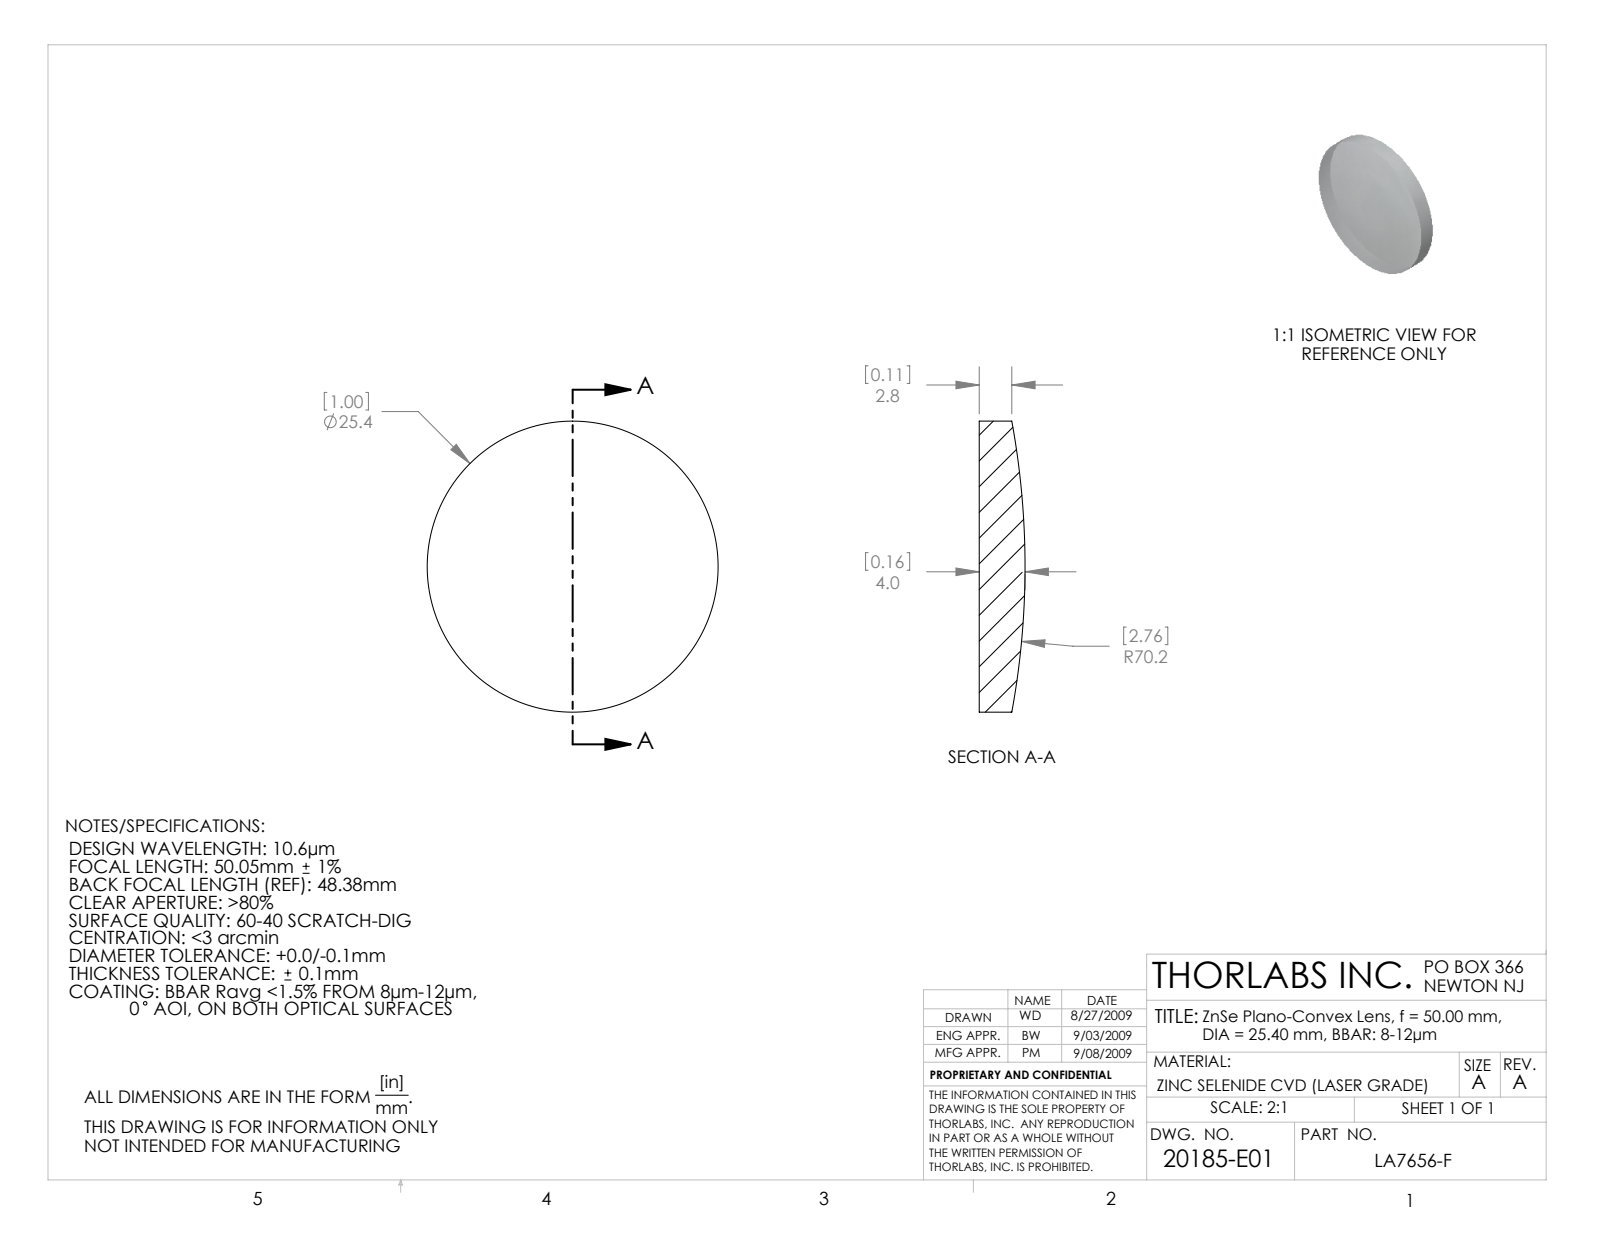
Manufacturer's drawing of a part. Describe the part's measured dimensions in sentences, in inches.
The part is named "20185-E0W". Its 3-D file was written by "SolidWorks 2007 (CONFIG_CONTROL_DESIGN)". It is 1 solid with 5 faces: 1 planar, 2 cylindrical and 2 other. Overall it measures 1 by 1 by 0.157 inches. Its volume is 0.106 cubic inches and its surface area 1.928 square inches. Round bosses or shafts: 1 of diameter 1.
